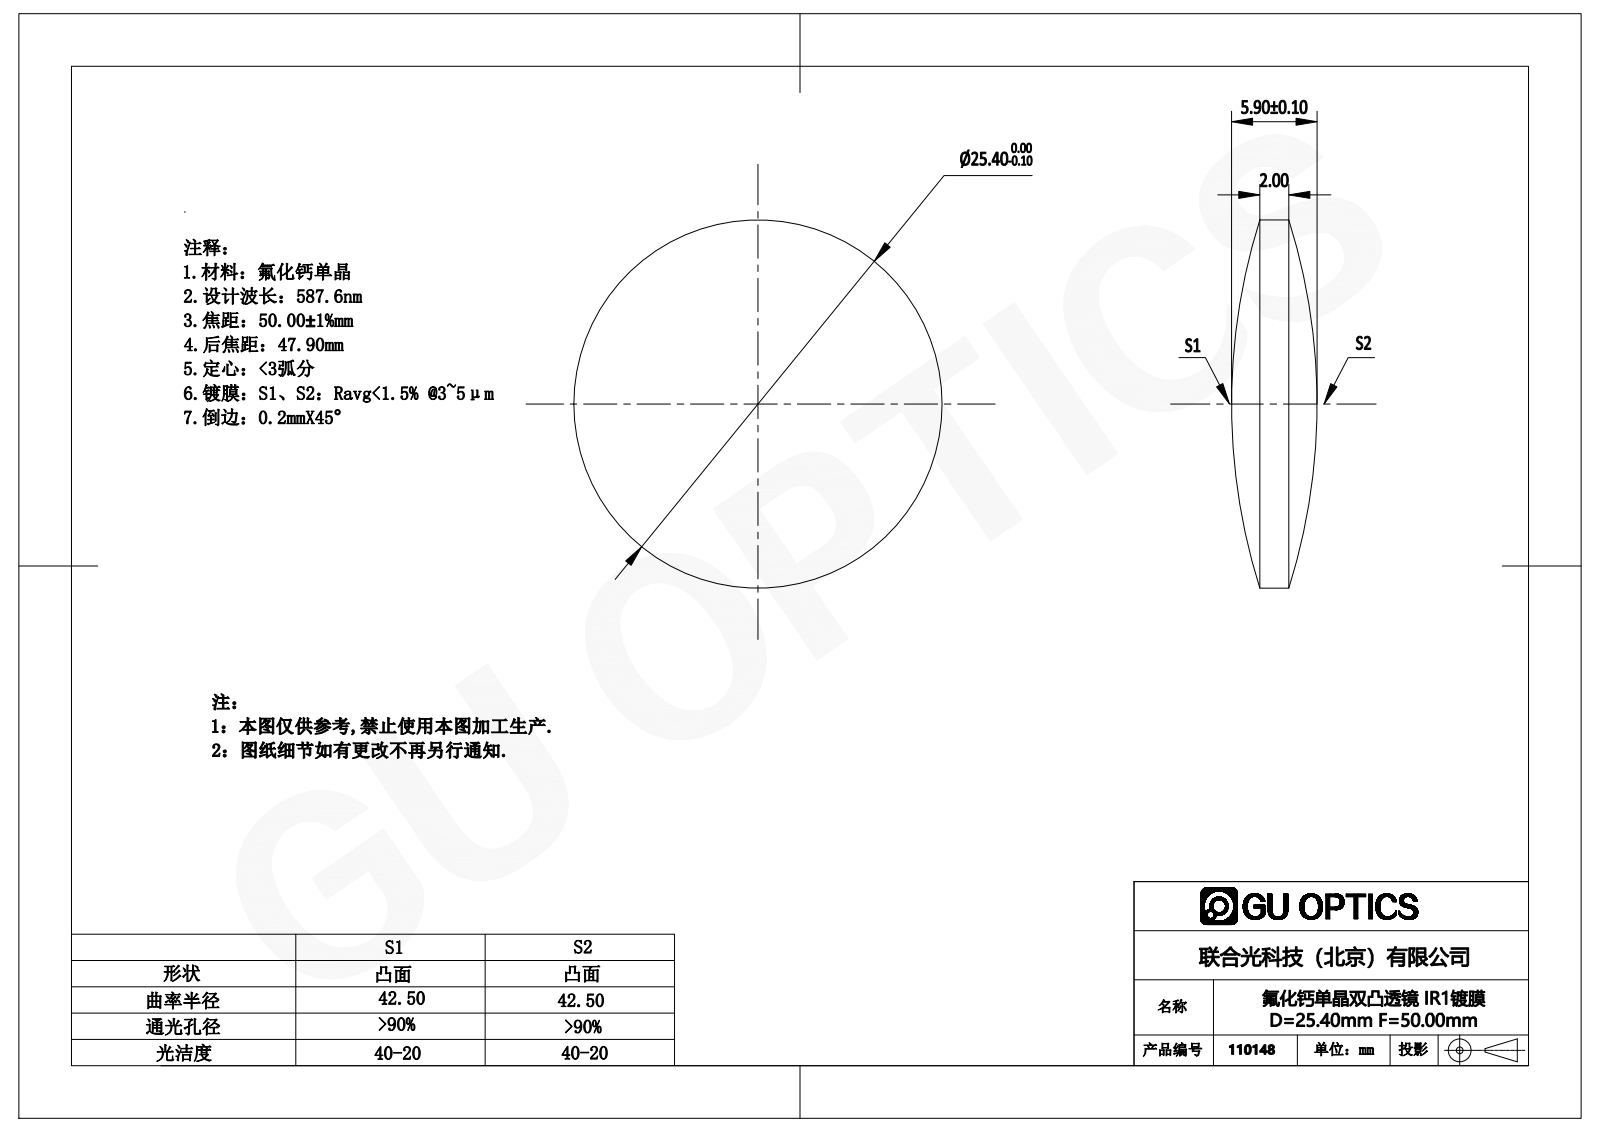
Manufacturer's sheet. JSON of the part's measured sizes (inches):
{"part_name": "110140", "step_written_by": "SolidWorks 2016 (CONFIG_CONTROL_DESIGN)", "units": "inches", "bodies": {"solids": 1, "faces": 6, "planar": 0, "cylindrical": 2, "other": 4}, "overall_size": [1, 1, 0.232], "volume_in3": 0.123, "surface_area_in2": 1.855, "round_bosses_or_shafts": [[1, 1]]}
